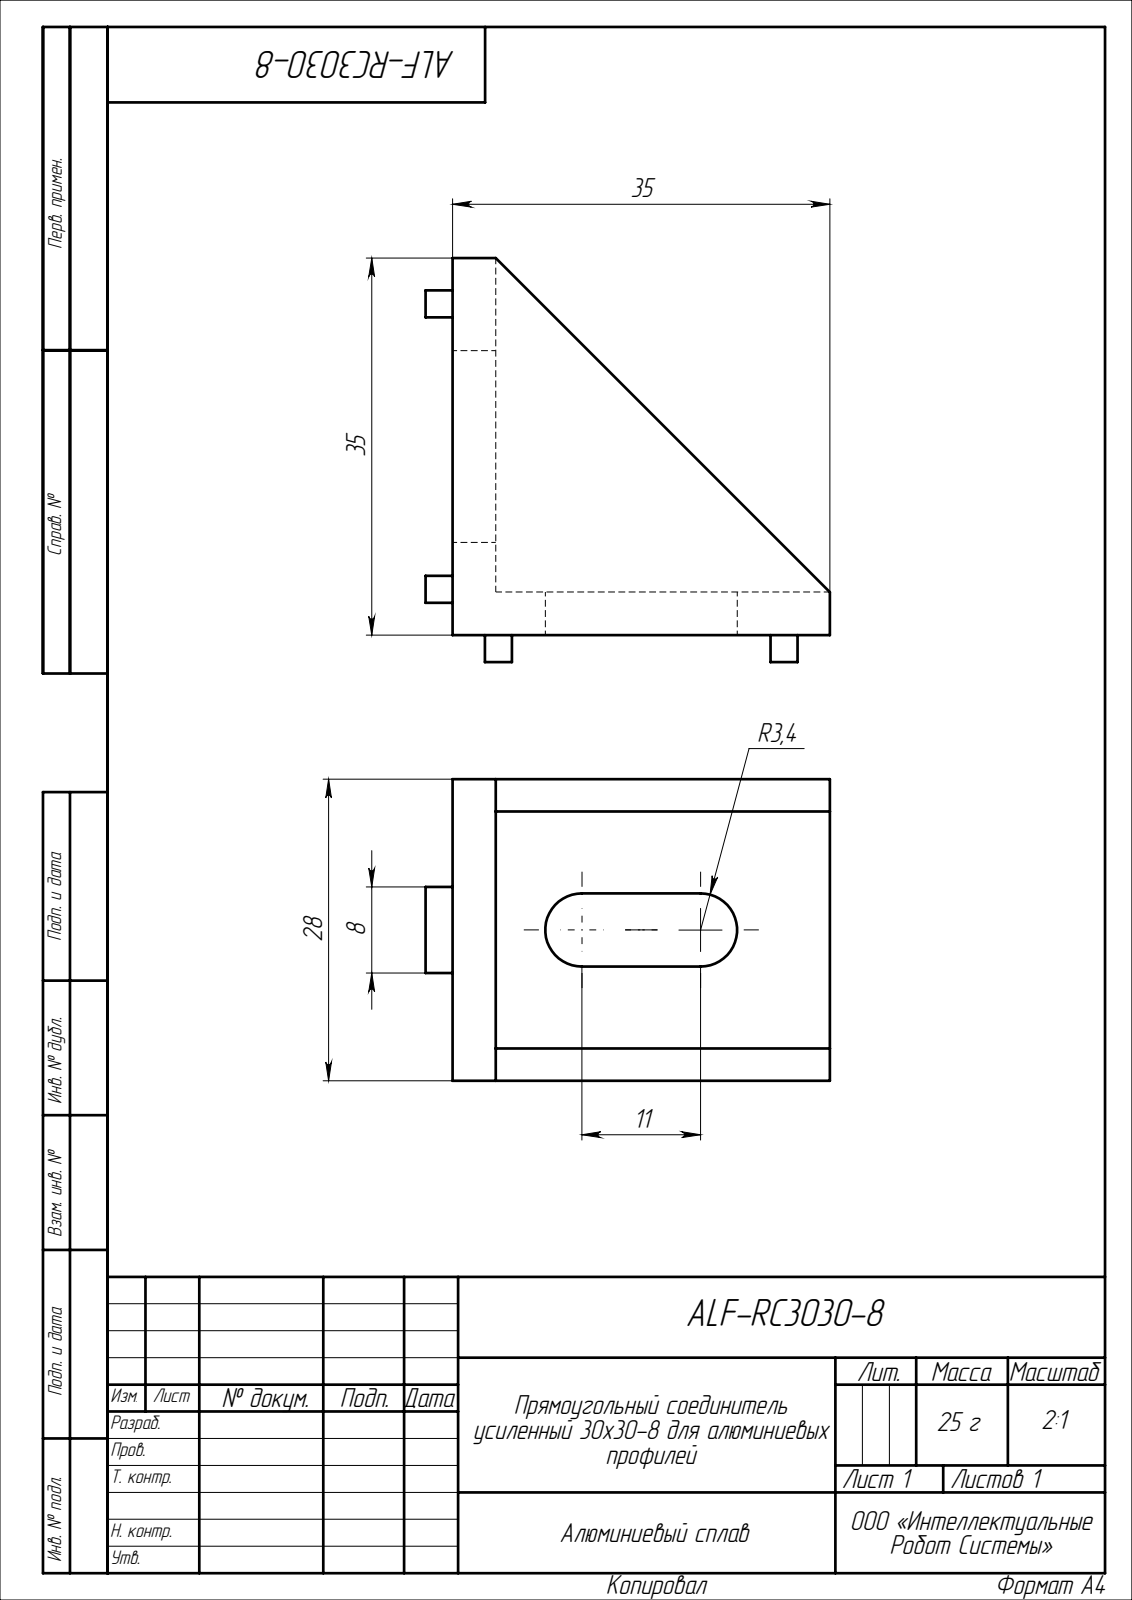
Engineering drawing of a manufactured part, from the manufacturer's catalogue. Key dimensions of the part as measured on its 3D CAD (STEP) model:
Part name (STEP PRODUCT): ALF-RC3030-8
STEP written by: SolidWorks 2022 (CONFIG_CONTROL_DESIGN)
Units: millimetres
Bodies: 1 solid, 41 faces (36 planar, 5 cylindrical, 0 other)
Overall size (bounding box): 37.5 × 37.5 × 28
Volume: 9 586 mm³ · Surface area: 6 373 mm²
Partial cylindrical surfaces — rounded edges, fillets, slot ends (radius × count): R3.4 ×4
Main face-to-face distances: 4, 3, 25, 28, 22, 35, 31, 10.6, 17.4, 7.6
